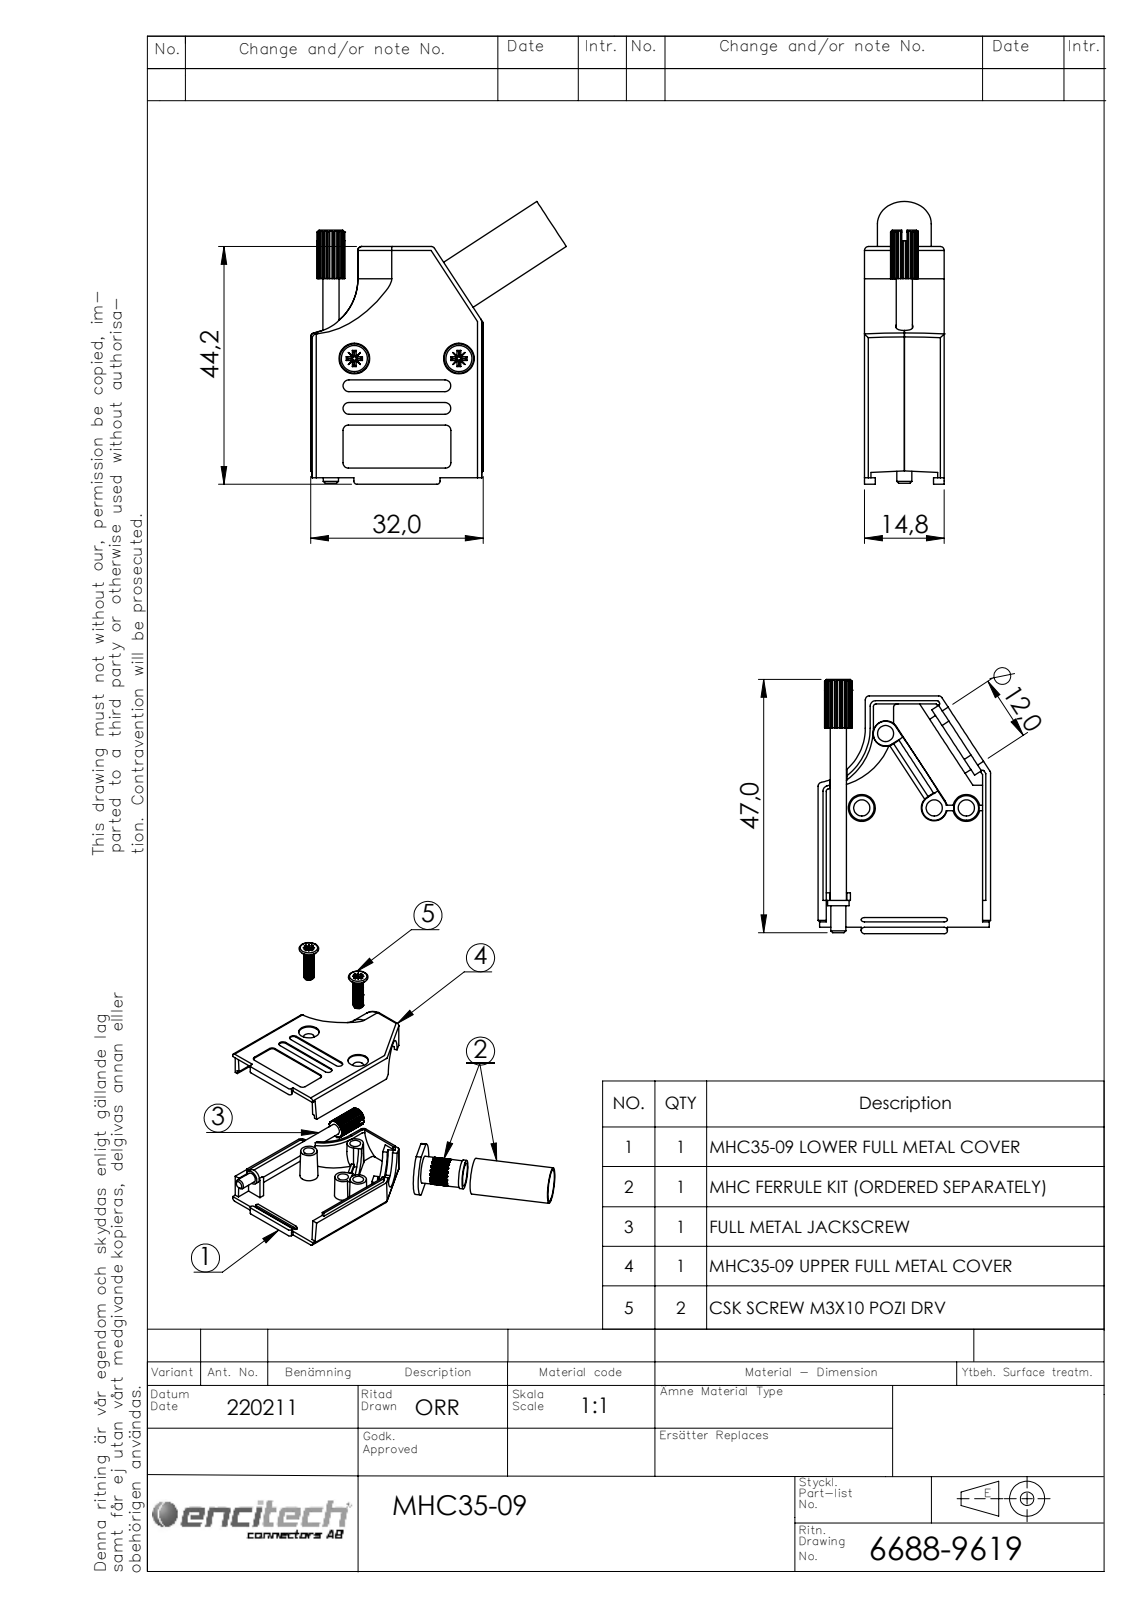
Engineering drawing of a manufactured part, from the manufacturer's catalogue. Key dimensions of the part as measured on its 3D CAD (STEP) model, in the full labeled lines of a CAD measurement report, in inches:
Part name (STEP PRODUCT): 6560-0138-11; 6824-0120-02; 6522-0110-12; 6855-0117-03 (+3 more)
STEP written by: SolidWorks 2021 (AUTOMOTIVE_DESIGN)
Units: inches
Bodies: 7 solids, 1572 faces (308 planar, 392 cylindrical, 872 other)
Overall size (bounding box): 2.068 × 1.867 × 0.583
Volume: 0.383 in³ · Surface area: 18.48 in²
Round holes (diameter × count): ⌀0.118 ×4, ⌀0.189 ×2, ⌀0.224 ×2, ⌀0.126 ×1, ⌀0.256 ×1, ⌀0.346 ×1, ⌀0.472 ×1
Round bosses / shafts (diameter × count): ⌀0.114 ×2, ⌀0.394 ×1, ⌀0.315 ×1, ⌀0.295 ×1, ⌀0.228 ×1, ⌀0.157 ×1, ⌀0.118 ×1, ⌀0.11 ×1
Partial cylindrical surfaces — rounded edges, fillets, slot ends (radius × count): R0.03 ×11, R0.004 ×8, R0.039 ×6, R0.043 ×4, R0.012 ×3, R0.02 ×2, R0.024 ×2, R0.102 ×1
Main face-to-face distances: 0.047, 0.535, 0.488, 0.583, 0.035, 0.571, 0.524, 0.244, 0.291, 1.258
Hole centre spacings: 0.235, 0.529, 0.571, 0.649, 0.764, 0.802
